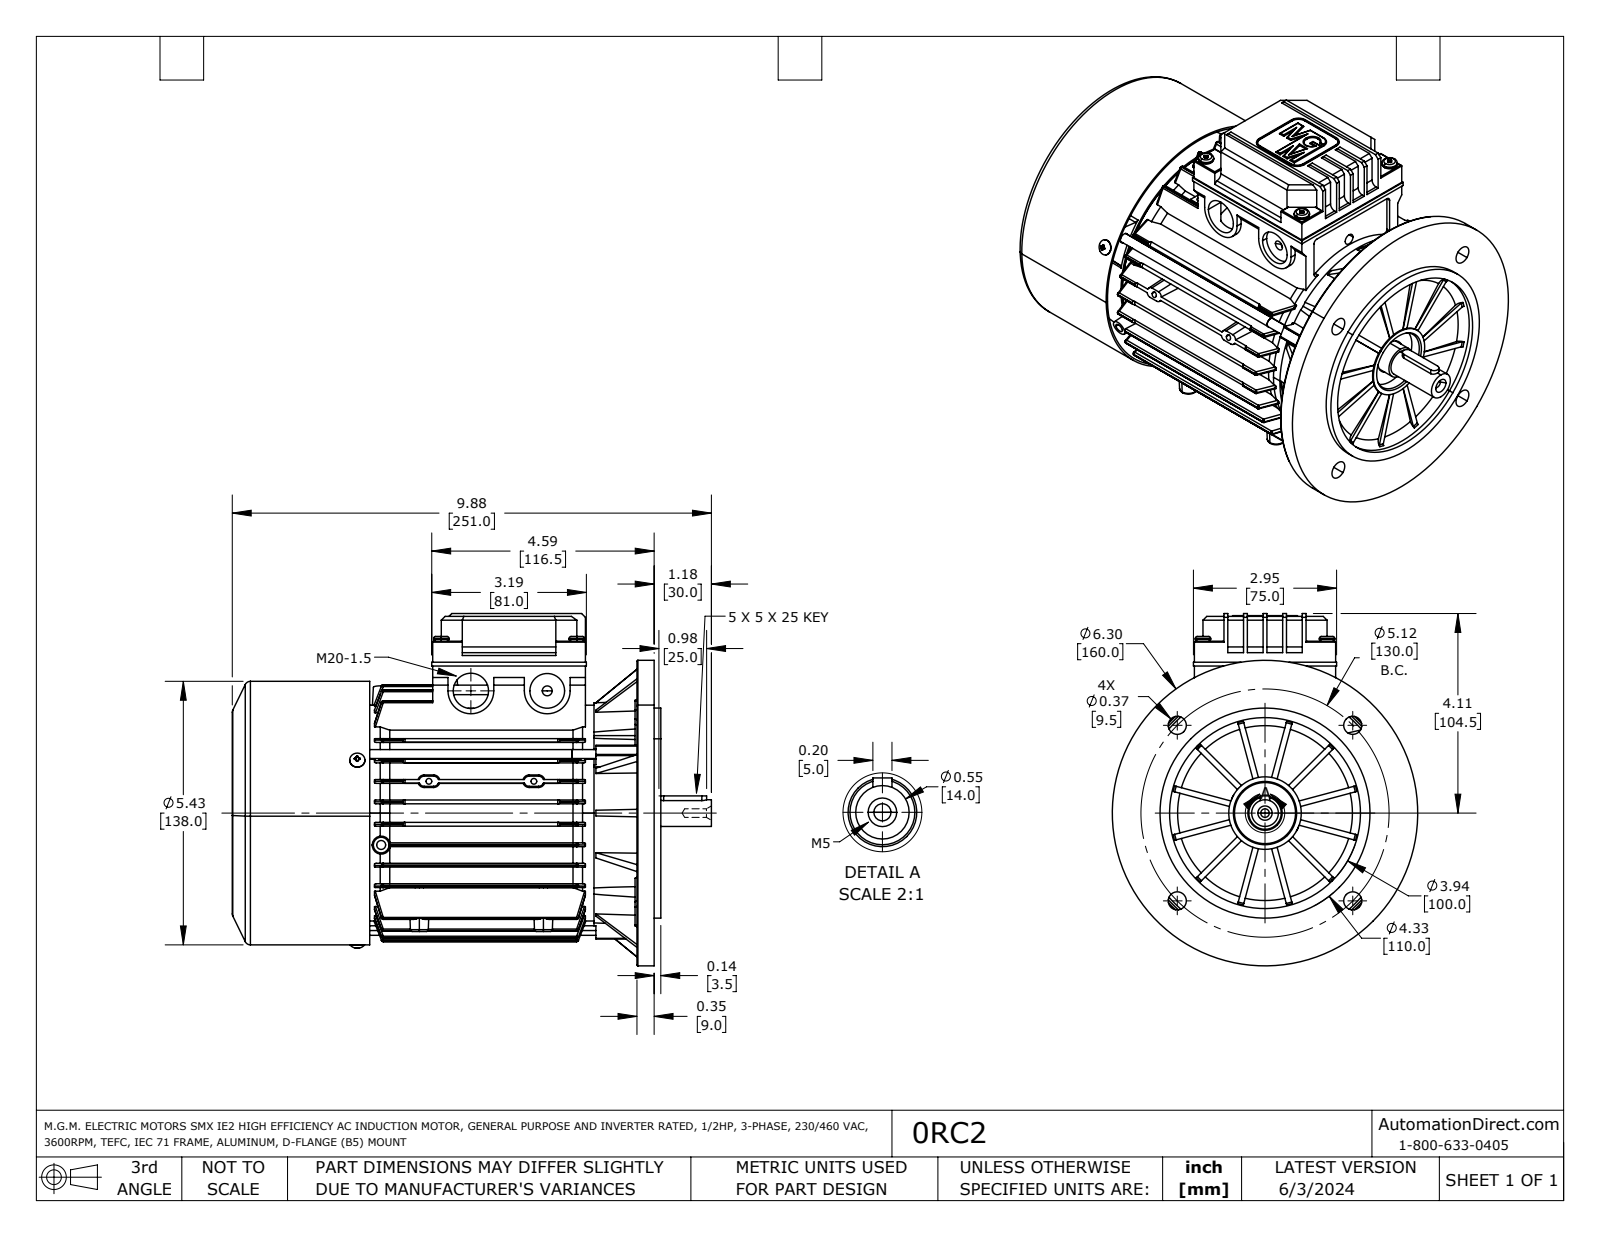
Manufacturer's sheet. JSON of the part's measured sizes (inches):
{"part_name": "0RC2", "step_written_by": "SolidWorks 2021 (AUTOMOTIVE_DESIGN)", "units": "inches", "bodies": {"solids": 21, "faces": 3305, "planar": 1108, "cylindrical": 1100, "other": 1097}, "overall_size": [9.882, 7.264, 6.299], "volume_in3": 37.75, "surface_area_in2": 694.2, "round_holes": [[0.118, 14], [0.13, 7], [0.217, 7], [0.157, 4], [0.177, 4], [0.236, 4], [0.374, 4], [0.126, 3], [0.165, 3], [0.276, 3], [0.185, 2], [0.228, 1]], "round_bosses_or_shafts": [[0.118, 10], [0.315, 7], [0.138, 4], [0.197, 3], [0.079, 3], [6.299, 1], [5.433, 1], [4.449, 1]], "partial_cylinders_radius": [[0.039, 252], [0.035, 60], [0.016, 36], [0.02, 36], [0.008, 32], [0.004, 16], [0.033, 16], [0.079, 6]], "face_to_face_distances": [0.422, 0.079, 0.843, 1.726, 0.343, 2.148, 0.5, 1.305, 2.57, 1.805], "hole_center_spacings": [2.559, 2.421, 4.211, 0.452, 0.458, 0.539, 0.768, 1.122]}
